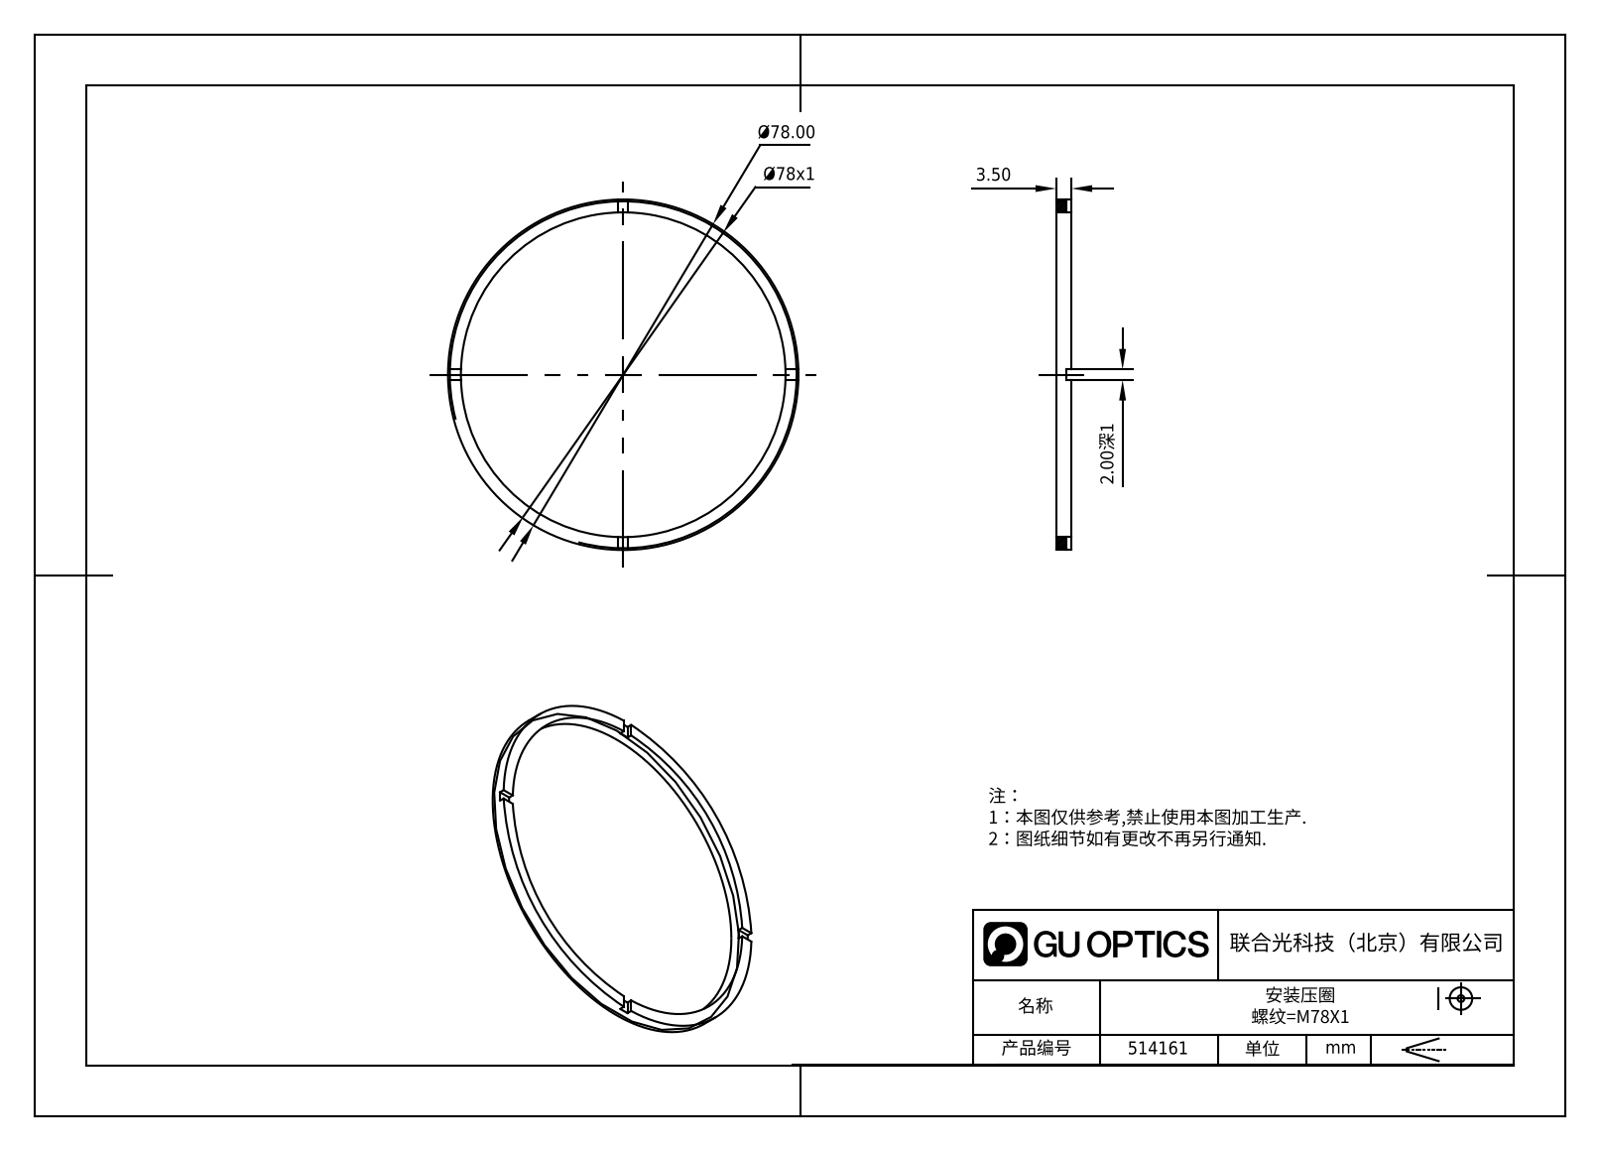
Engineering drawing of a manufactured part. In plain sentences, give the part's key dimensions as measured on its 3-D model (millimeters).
The part is named "514161". Its 3-D file was written by "SolidWorks 2020 (CONFIG_CONTROL_DESIGN)". It is 1 solid with 21 faces: 17 planar, 4 cylindrical and 0 other. Overall it measures 78 by 78 by 3.5 millimeters. Its volume is 2 450 cubic millimeters and its surface area 3 071 square millimeters. Round holes: 1 of diameter 72. Round bosses or shafts: 1 of diameter 78. The main face-to-face distances are 3.5, 2.5, 1, 2.
